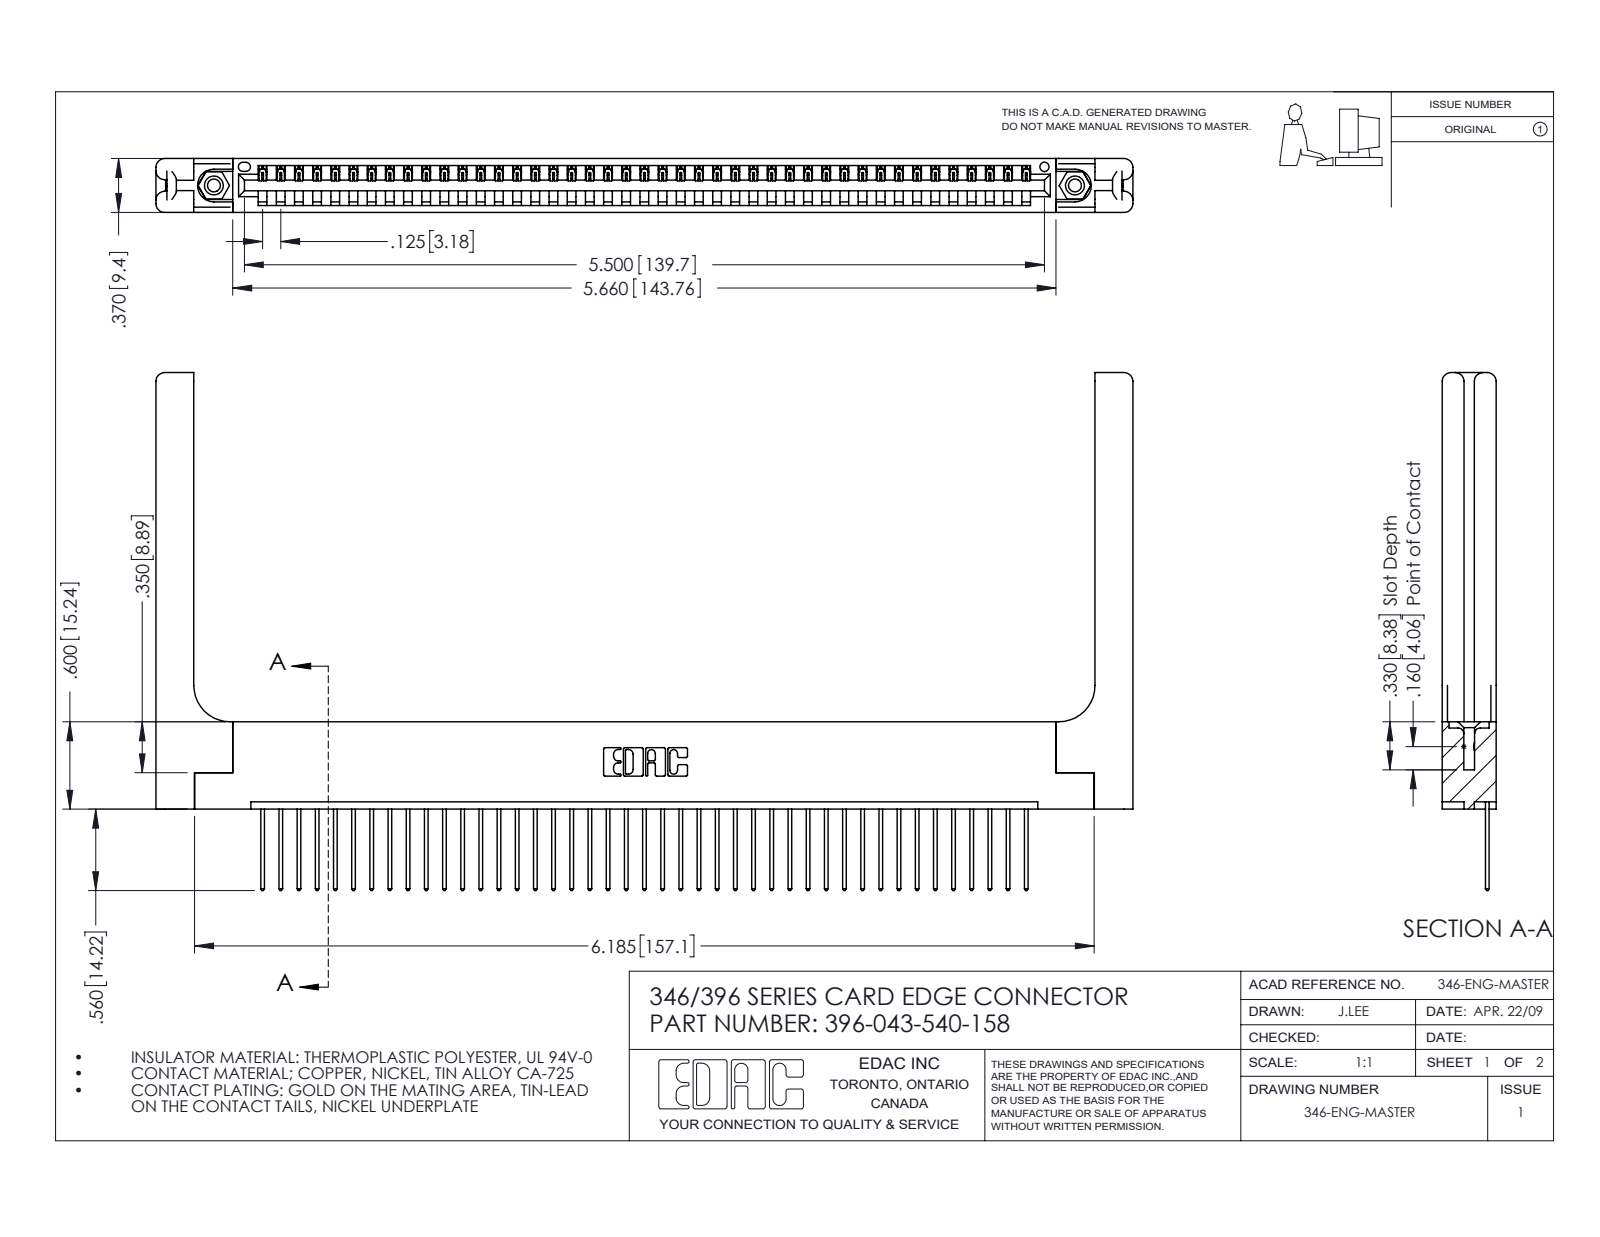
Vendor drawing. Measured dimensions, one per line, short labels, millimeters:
name: 346-220-058_345-220-058; 345-250-001_345-250-001-102; 345-292-001_345-293-140; 346 Part_Flush Mounting Lugs - 0.156 Dia-TH (+1 more)
written by: SolidWorks 2016 (CONFIG_CONTROL_DESIGN)
unit: mm
bodies: 48 solids, 2872 faces (1944 planar, 868 cylindrical, 60 other)
size: 170.6 × 90.4 × 9.4
volume: 23 910 mm³; area: 26 100 mm²
holes: 2× ⌀2.3, 2× ⌀3.2, 2× ⌀4, 1× ⌀1.6
bosses: 2× ⌀3.9
rounds: 86× R0.2, 86× R0.3, 22× R0.3, 16× R1.5, 6× R0.2, 6× R0.8, 3× R0.7, 2× R0.8
face distances: 9.4, 1.2, 8.2, 1.8, 3.8, 3.8, 6.4, 7.6, 0.6, 5.6
hole spacings: 6.2, 145.1, 150.4
